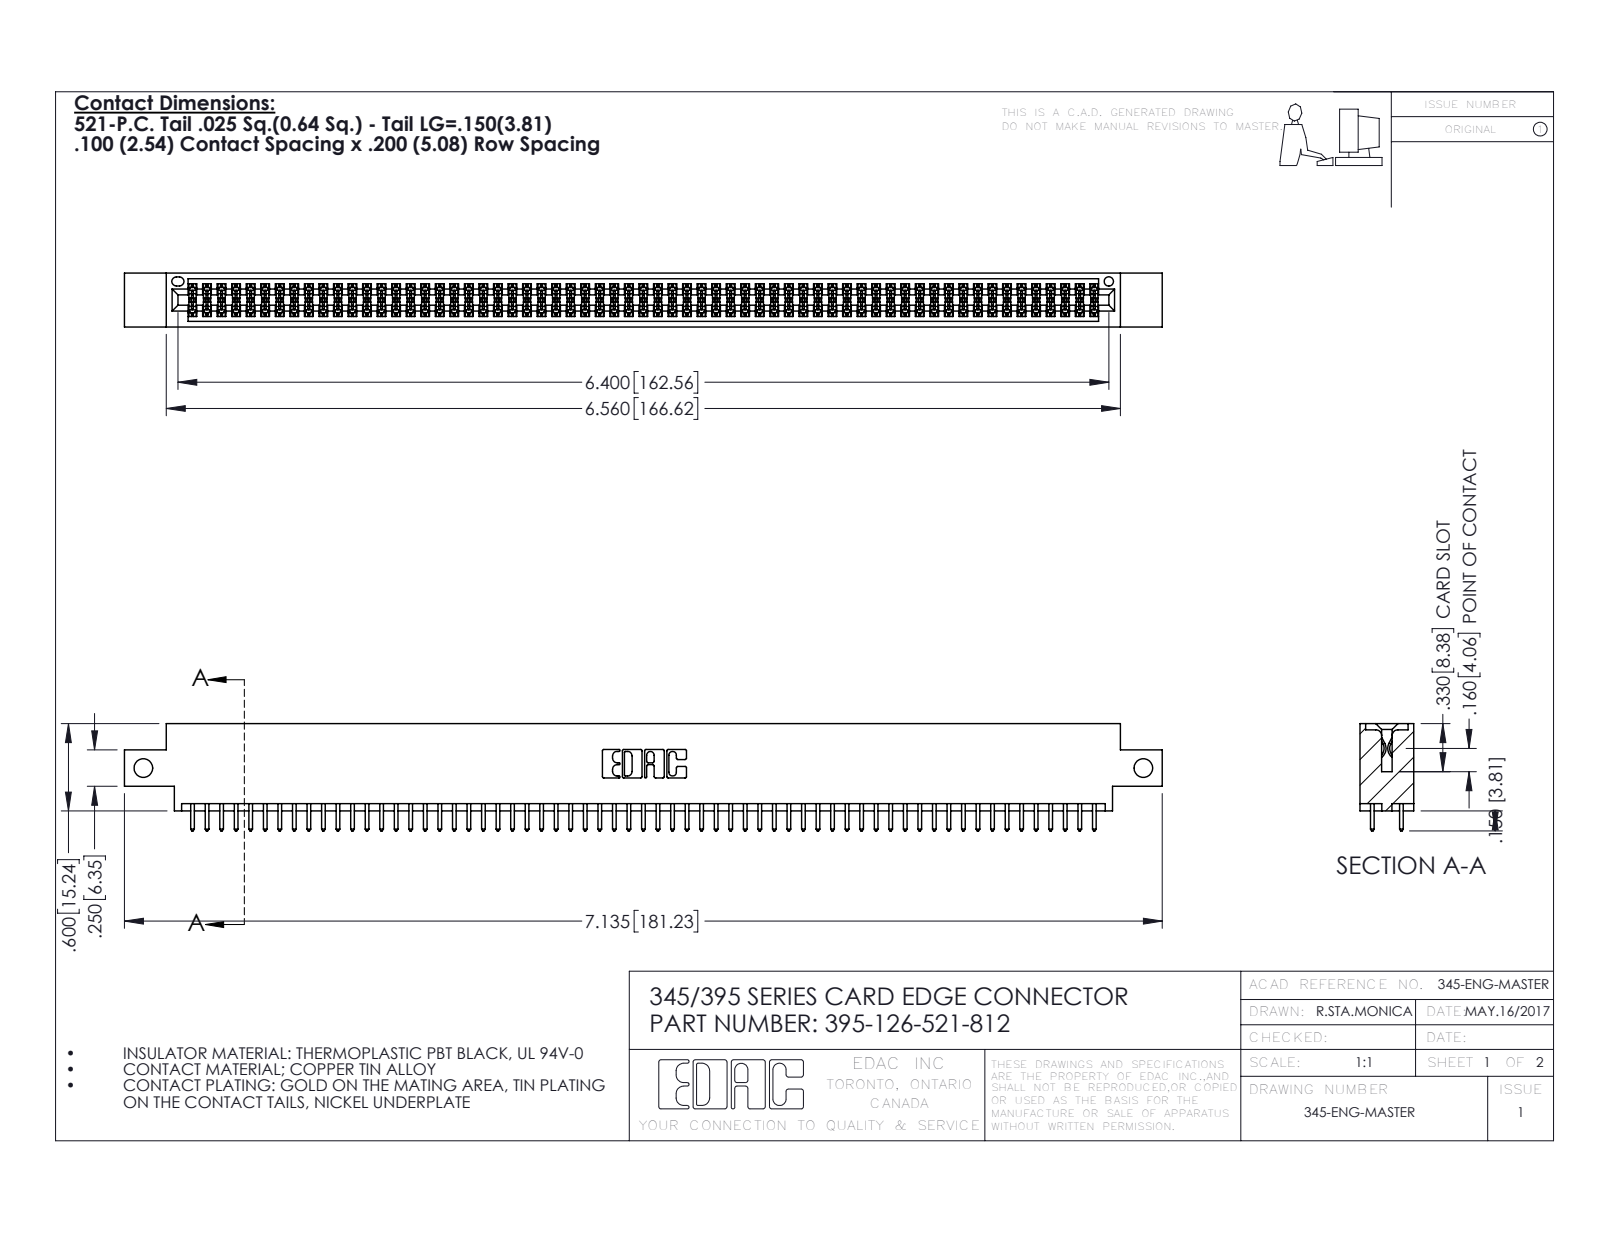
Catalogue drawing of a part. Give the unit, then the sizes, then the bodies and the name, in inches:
Units: inches
Overall size (bounding box): 7.135 × 0.737 × 0.37
Round holes (diameter × count): ⌀0.128 ×2, ⌀0.064 ×1
Partial cylindrical surfaces — rounded edges, fillets, slot ends (radius × count): R0.006 ×189, R0.01 ×126, R0.01 ×22, R0.007 ×6, R0.031 ×6, R0.026 ×3, R0.014 ×2, R0.019 ×2
Main face-to-face distances: 0.072, 0.298, 0.2, 0.37, 0.098, 0.272, 0.025, 0.225, 0.175, 0.149
Hole centre spacings: 6.875
Volume: 1.071 in³ · Surface area: 40.33 in²
Bodies: 127 solids, 6430 faces (4242 planar, 2188 cylindrical, 0 other)
Part name (STEP PRODUCT): 345 Part_0.170 Offset - Side Mount; 345-292-001_345-293-121; 395-126-521-812
STEP written by: SolidWorks 2016 (CONFIG_CONTROL_DESIGN)
